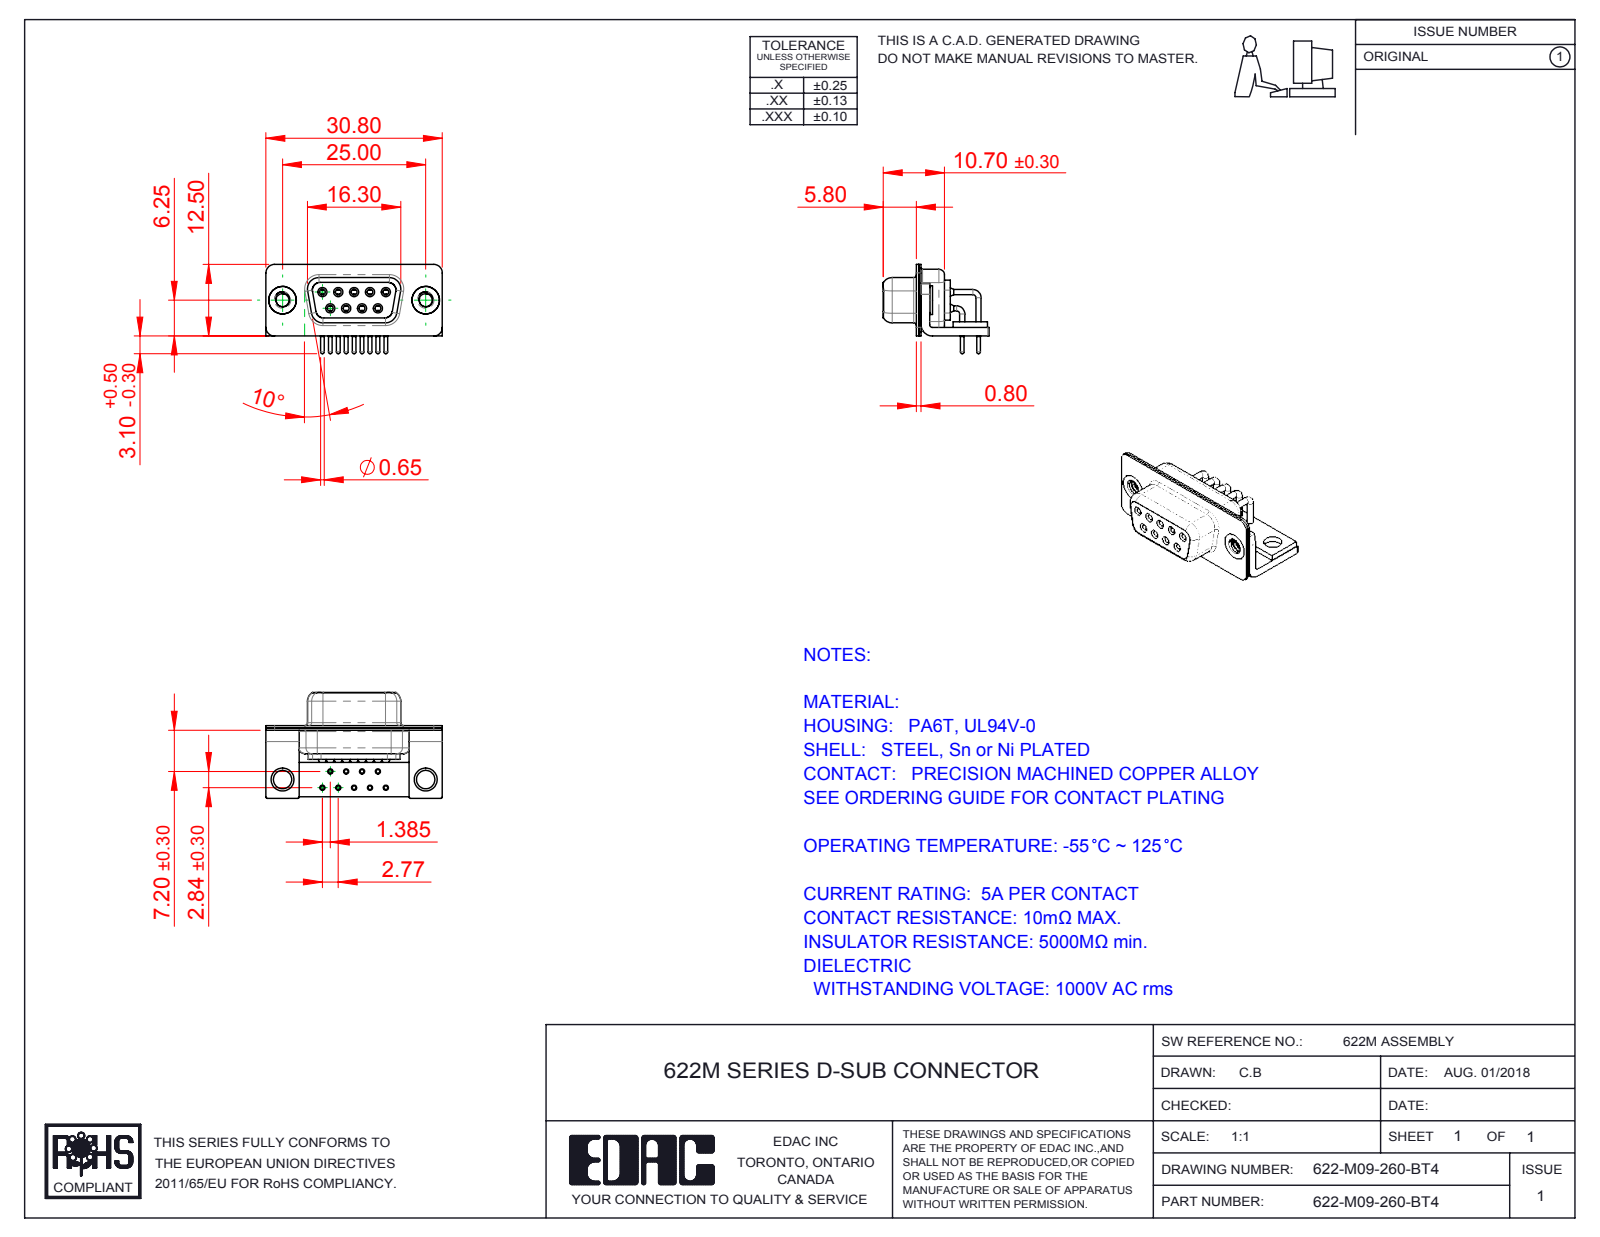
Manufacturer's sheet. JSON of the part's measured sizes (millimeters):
{"part_name": "622-M09-260-BT4; 622M Stabilizer Board_09 Contacts; 622M Stabilizer Bracket; 622M 4-40 Threaded Rivet_Stabilizer (+5 more)", "step_written_by": "SolidWorks 2016 (CONFIG_CONTROL_DESIGN)", "units": "millimeters", "bodies": {"solids": 17, "faces": 824, "planar": 228, "cylindrical": 384, "other": 212}, "overall_size": [30.8, 18.5, 15.6], "volume_mm3": 2131, "surface_area_mm2": 5520, "round_holes": [[0.9, 9], [1, 9], [1.1, 9], [1.7, 9], [1.8, 9], [2, 9], [2.26, 2], [3.2, 2], [4, 2], [4.8, 2]], "round_bosses_or_shafts": [[1.6, 9], [1.5, 9], [0.9, 9], [0.65, 9], [5, 2], [4.9, 2]], "partial_cylinders_radius": [[0.25, 16], [1.5, 16], [2, 13], [1.35, 8], [1.6, 8], [0.5, 5], [0.6, 4], [0.65, 4]], "face_to_face_distances": [0.4, 0.8, 2.3, 1.5, 1.9, 1, 9.35, 1.45, 8.95, 0.85], "hole_center_spacings": [3.16, 2.77, 5.54, 5.03, 5.04, 8.31, 7.48, 7.49]}
